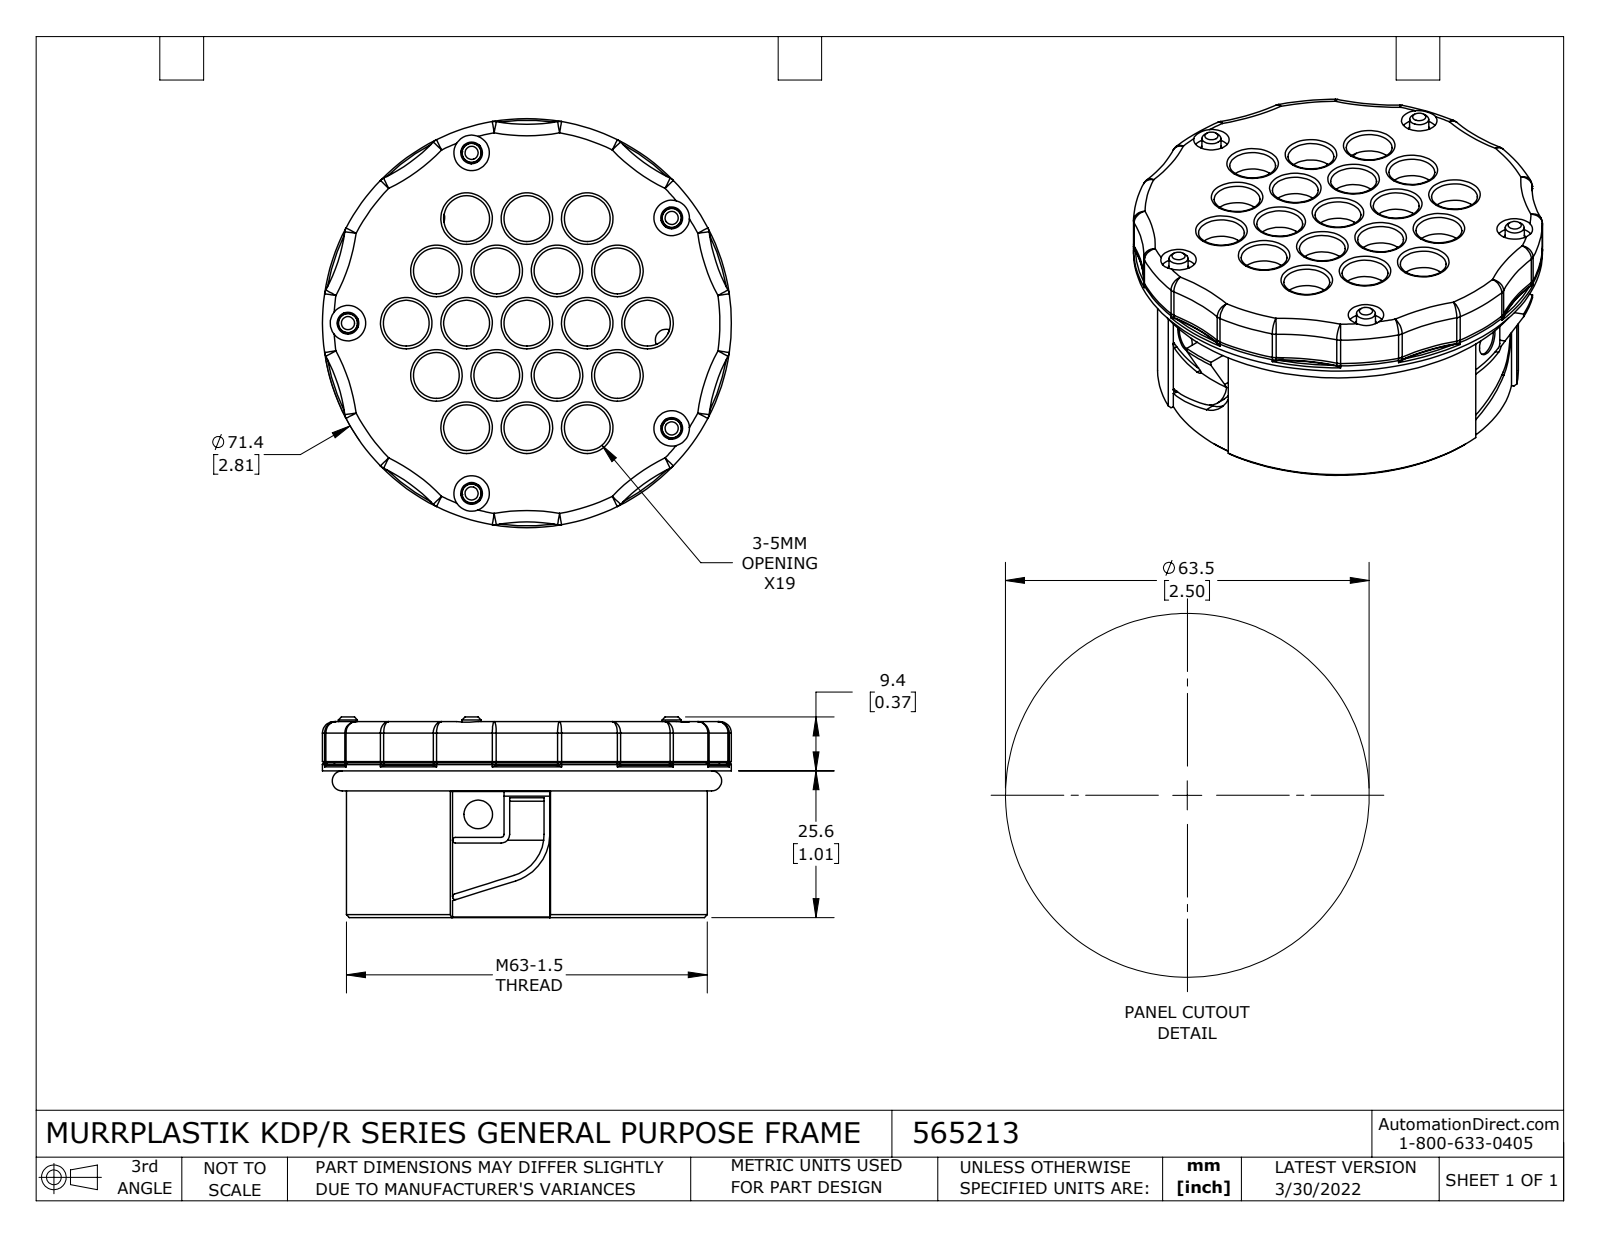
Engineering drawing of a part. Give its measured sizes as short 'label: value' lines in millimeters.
name: 565213
written by: SolidWorks 2021 (CONFIG_CONTROL_DESIGN)
unit: mm
bodies: 6 solids, 620 faces (89 planar, 284 cylindrical, 247 other)
size: 71.4 × 71.4 × 35
volume: 46 224 mm³; area: 46 174 mm²
holes: 19× ⌀8, 8× ⌀3.8, 5× ⌀6.2, 3× ⌀5, 2× ⌀4, 1× ⌀54.9, 1× ⌀58, 1× ⌀67.4
bosses: 2× ⌀4.8, 1× ⌀71.4, 1× ⌀66.4, 1× ⌀64, 1× ⌀63, 1× ⌀61.7, 1× ⌀59, 1× ⌀55.7
rounds: 21× R2, 10× R30, 9× R0.5, 6× R0.3, 3× R1.5, 3× R7.5, 3× R8.5, 1× R2.4
face distances: 1.75, 3.5, 4, 7.5, 5.75, 4.7, 8.2, 6.45, 12.2, 1.6
hole spacings: 10.53, 18.24, 27.86, 21.06, 21.07, 27.87, 31.59, 37.97
